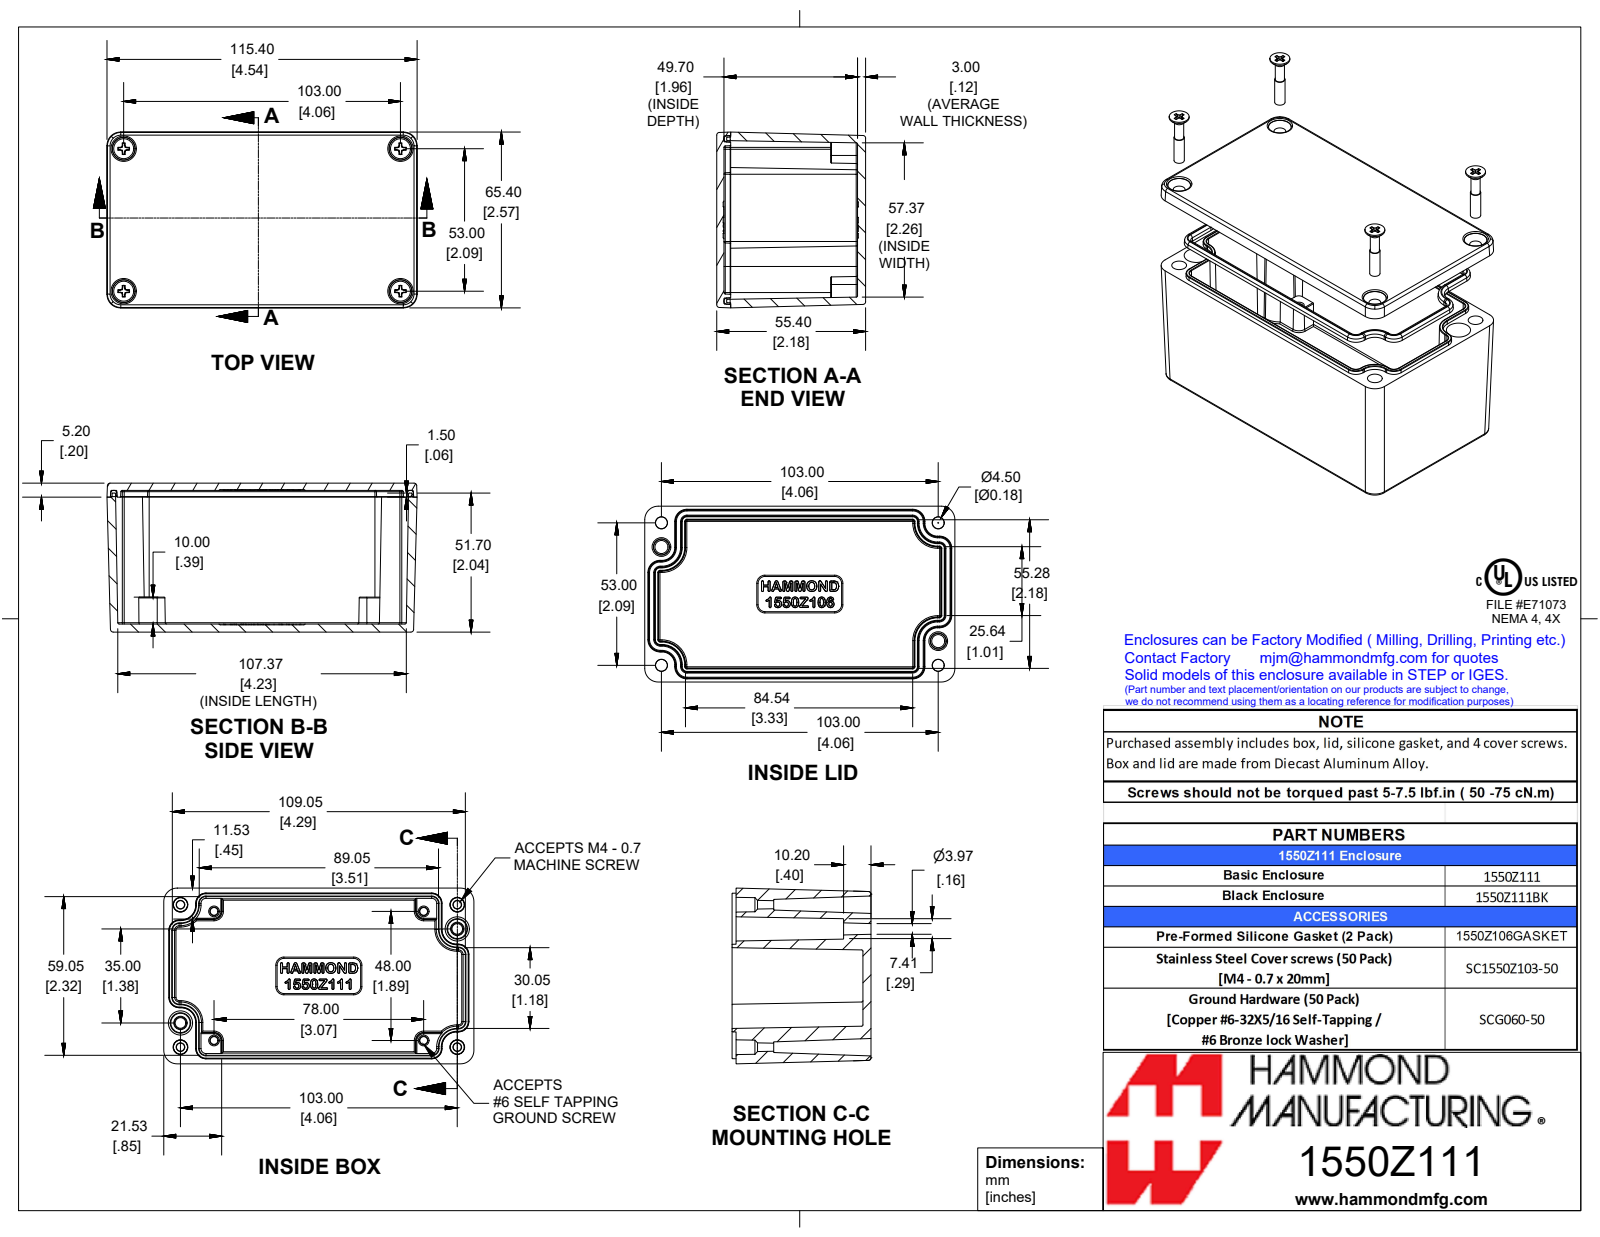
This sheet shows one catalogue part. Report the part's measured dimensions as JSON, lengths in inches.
{"part_name": "1550Z111", "step_written_by": "SolidWorks 2019 (AUTOMOTIVE_DESIGN)", "units": "inches", "bodies": {"solids": 7, "faces": 1374, "planar": 379, "cylindrical": 238, "other": 757}, "overall_size": [4.543, 2.575, 2.186], "volume_in3": 6.967, "surface_area_in2": 118.1, "round_bosses_or_shafts": [[0.295, 4], [0.154, 4], [0.13, 4]], "partial_cylinders_radius": [[0.008, 50], [0.02, 32], [0.039, 28], [0.012, 24], [0.197, 8]], "face_to_face_distances": [2.181, 0.106, 2.075, 0.118, 1.957, 2.063, 0.098, 1.976, 1.858, 0.205]}
